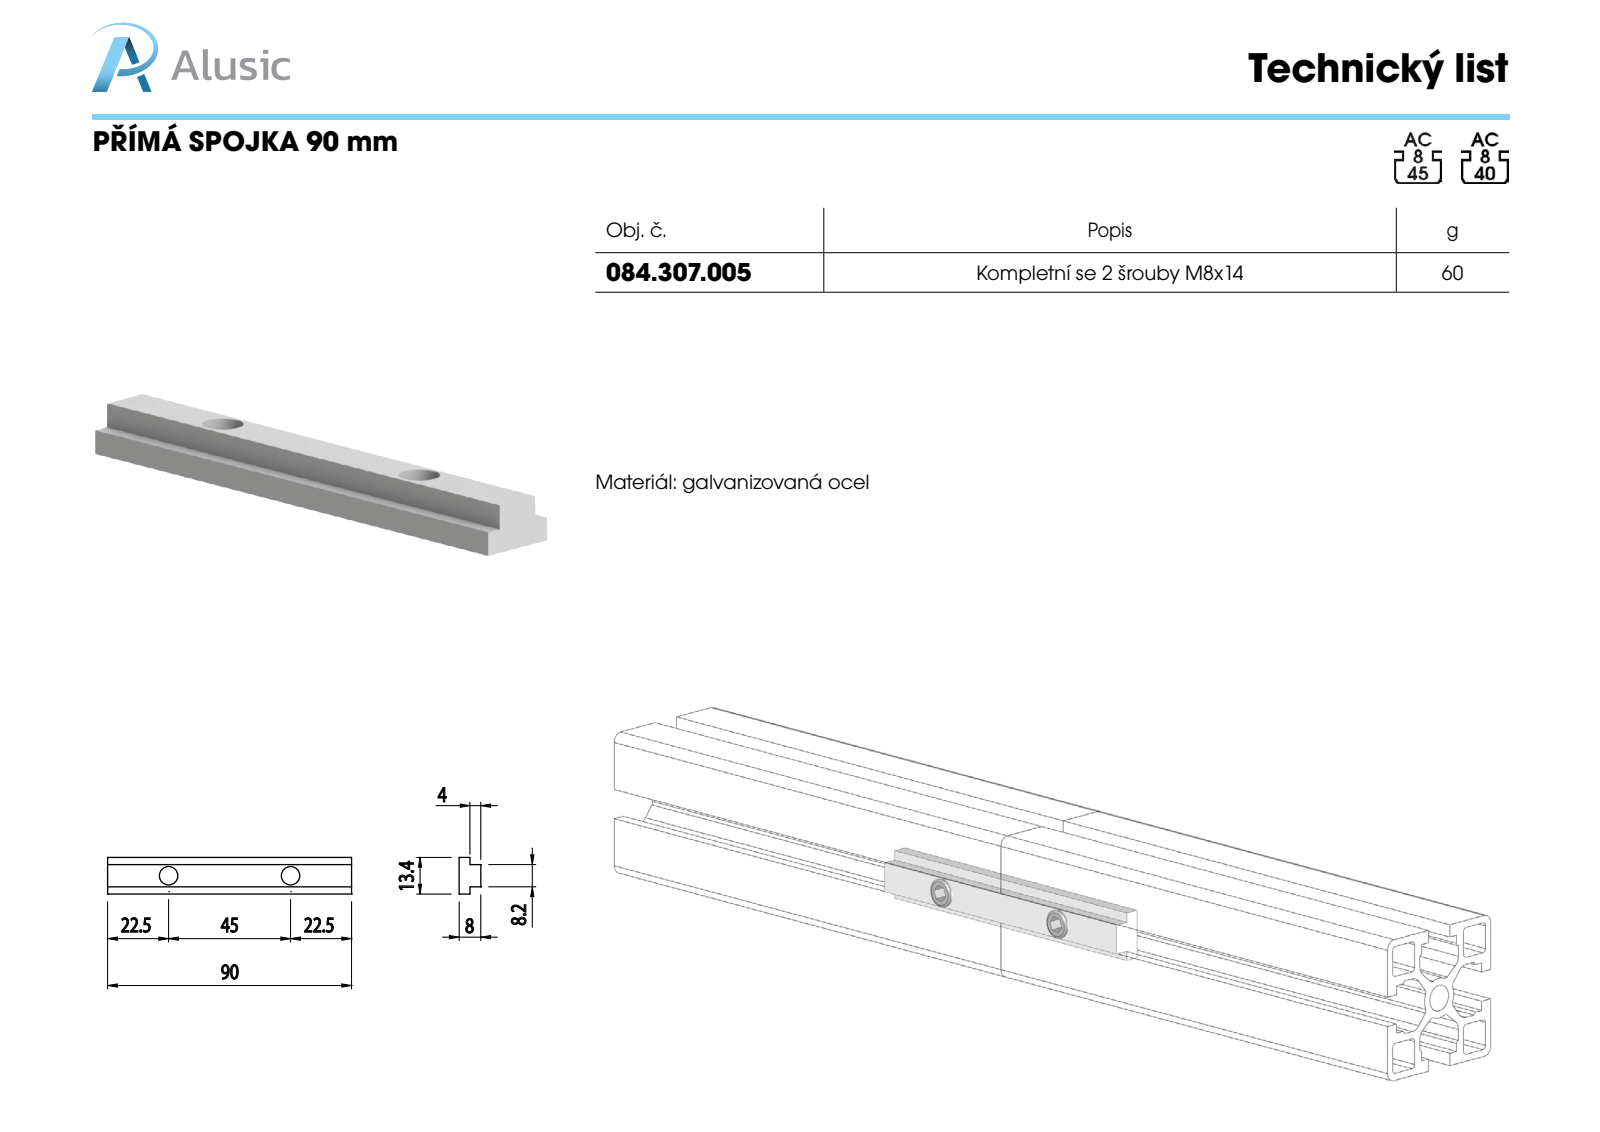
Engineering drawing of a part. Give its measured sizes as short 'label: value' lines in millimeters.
name: 084.307.005
written by: SolidWorks 2011 (CONFIG_CONTROL_DESIGN)
unit: mm
bodies: 1 solid, 14 faces (10 planar, 4 cylindrical, 0 other)
size: 90 × 13.5 × 8
volume: 7 231 mm³; area: 4 240 mm²
holes: 2× ⌀6.8
face distances: 4, 2.65, 10.85, 8, 8.2, 13.5, 90
hole spacings: 45
